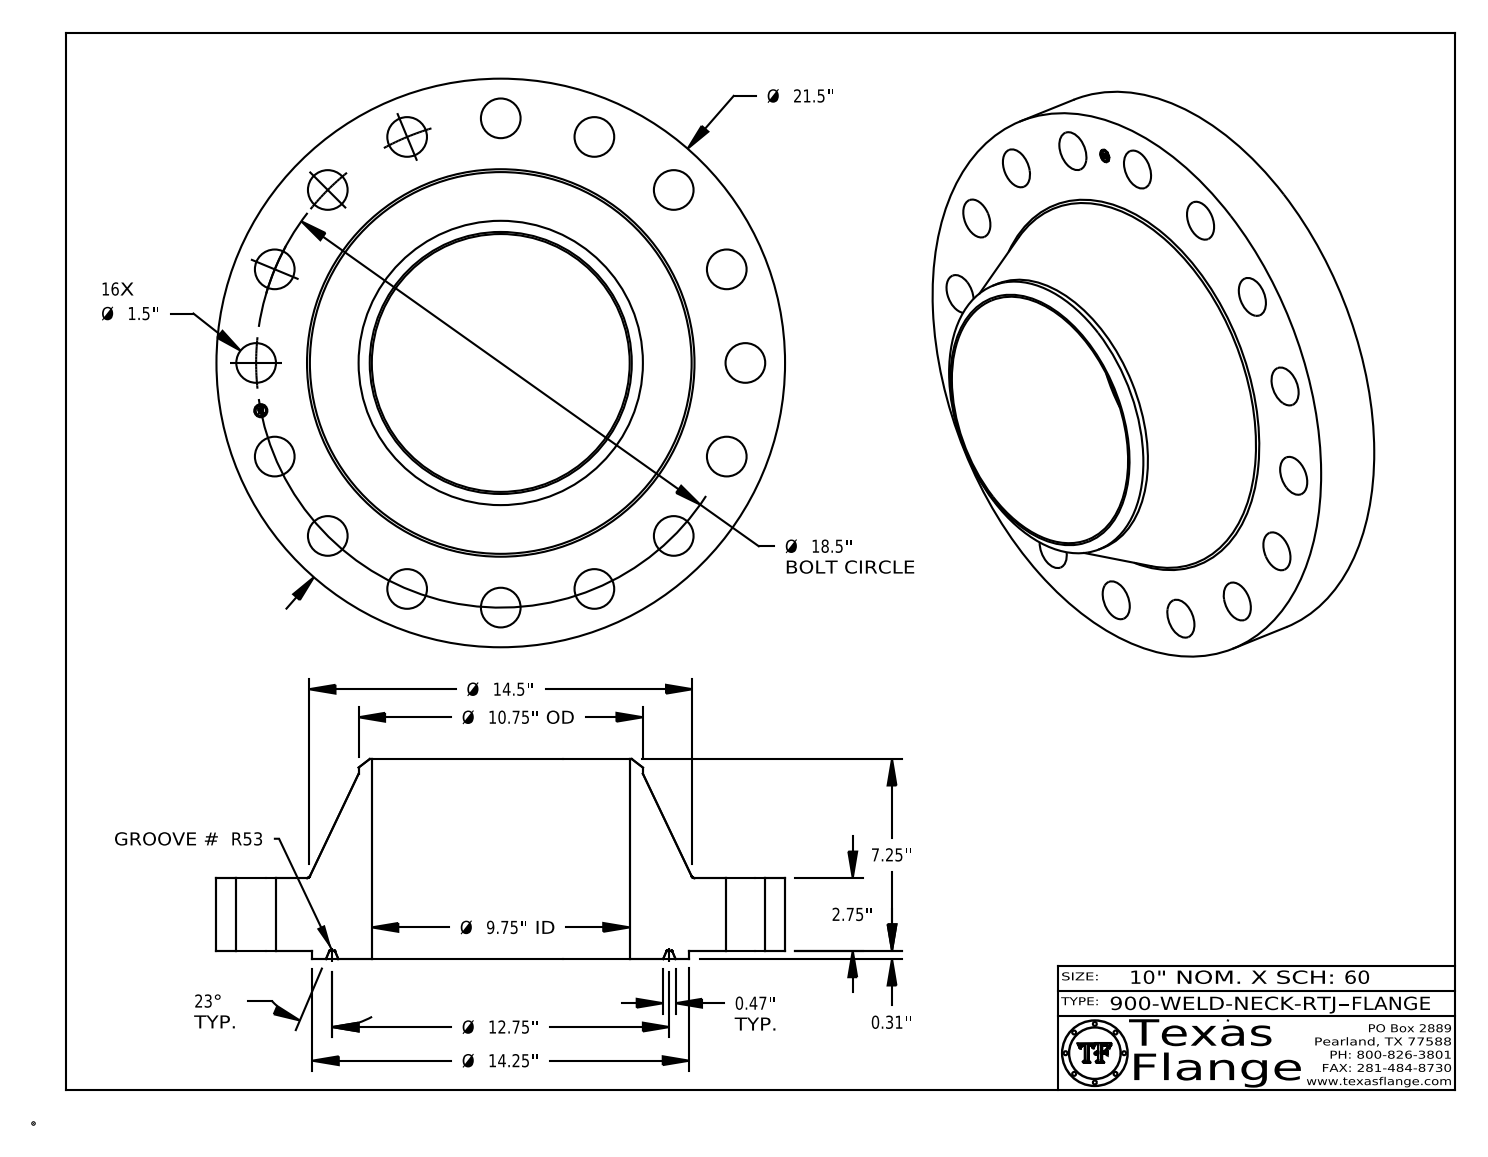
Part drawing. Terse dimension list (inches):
name: 900-WELD-NECK-RTJ
written by: CATIA V5 STEP AP214 (AUTOMOTIVE_DESIGN)
unit: in
bodies: 1 solid, 445 faces (371 planar, 60 cylindrical, 14 other)
size: 21.5 × 21.5 × 7.563
volume: 947.1 in³; area: 1 285 in²
holes: 16× ⌀1.5, 1× ⌀0.495, 1× ⌀9.75
bosses: 8× ⌀0.03, 1× ⌀21.5, 1× ⌀14.25, 1× ⌀10.75, 1× ⌀0.39
face distances: 2.75, 0.313, 3.063, 7.563, 7.25, 4.5, 3.048, 2.735, 0.015, 4.515
hole spacings: 15.382, 7.08, 9.25, 13.081, 3.609, 3.609, 10.278, 10.278
